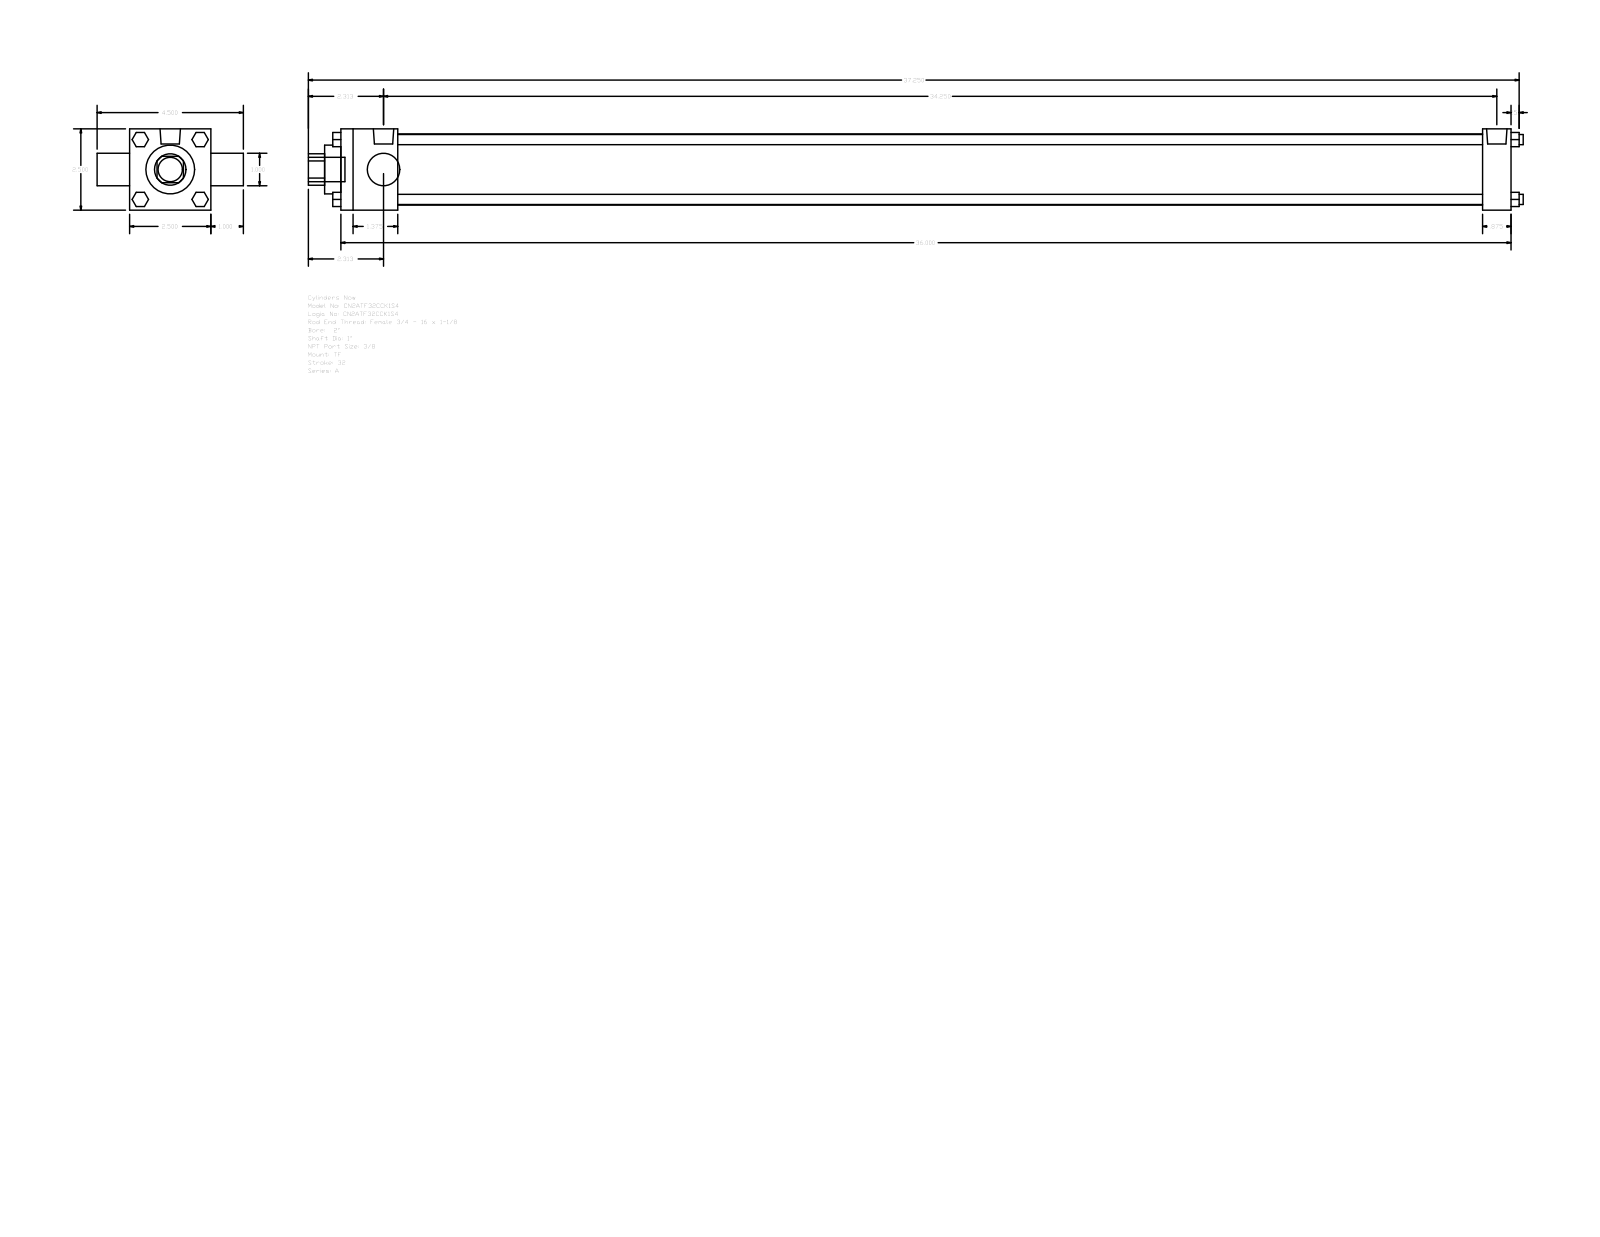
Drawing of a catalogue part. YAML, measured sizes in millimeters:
part_name: "A_TF__0200_1"
step_written_by: "GSSL Pune (CONFIG_CONTROL_DESIGN)"
units: millimeters
bodies: {solids: 0, faces: 120, planar: 92, cylindrical: 28, other: 0}
overall_size: [949.33, 114.3, 63.5]
round_holes:
  - {diameter: 25.4, count: 2}
  - {diameter: 38.1, count: 1}
  - {diameter: 55.63, count: 1}
round_bosses_or_shafts:
  - {diameter: 7.94, count: 4}
  - {diameter: 5.56, count: 3}
  - {diameter: 15.93, count: 2}
  - {diameter: 19.05, count: 1}
partial_cylinders:
  - {radius: 12.29, count: 1}
face_to_face_distances: [63.5, 914.4, 44.45, 892.18, 847.73, 869.95, 22.22, 25.4, 88.9, 927.1]
